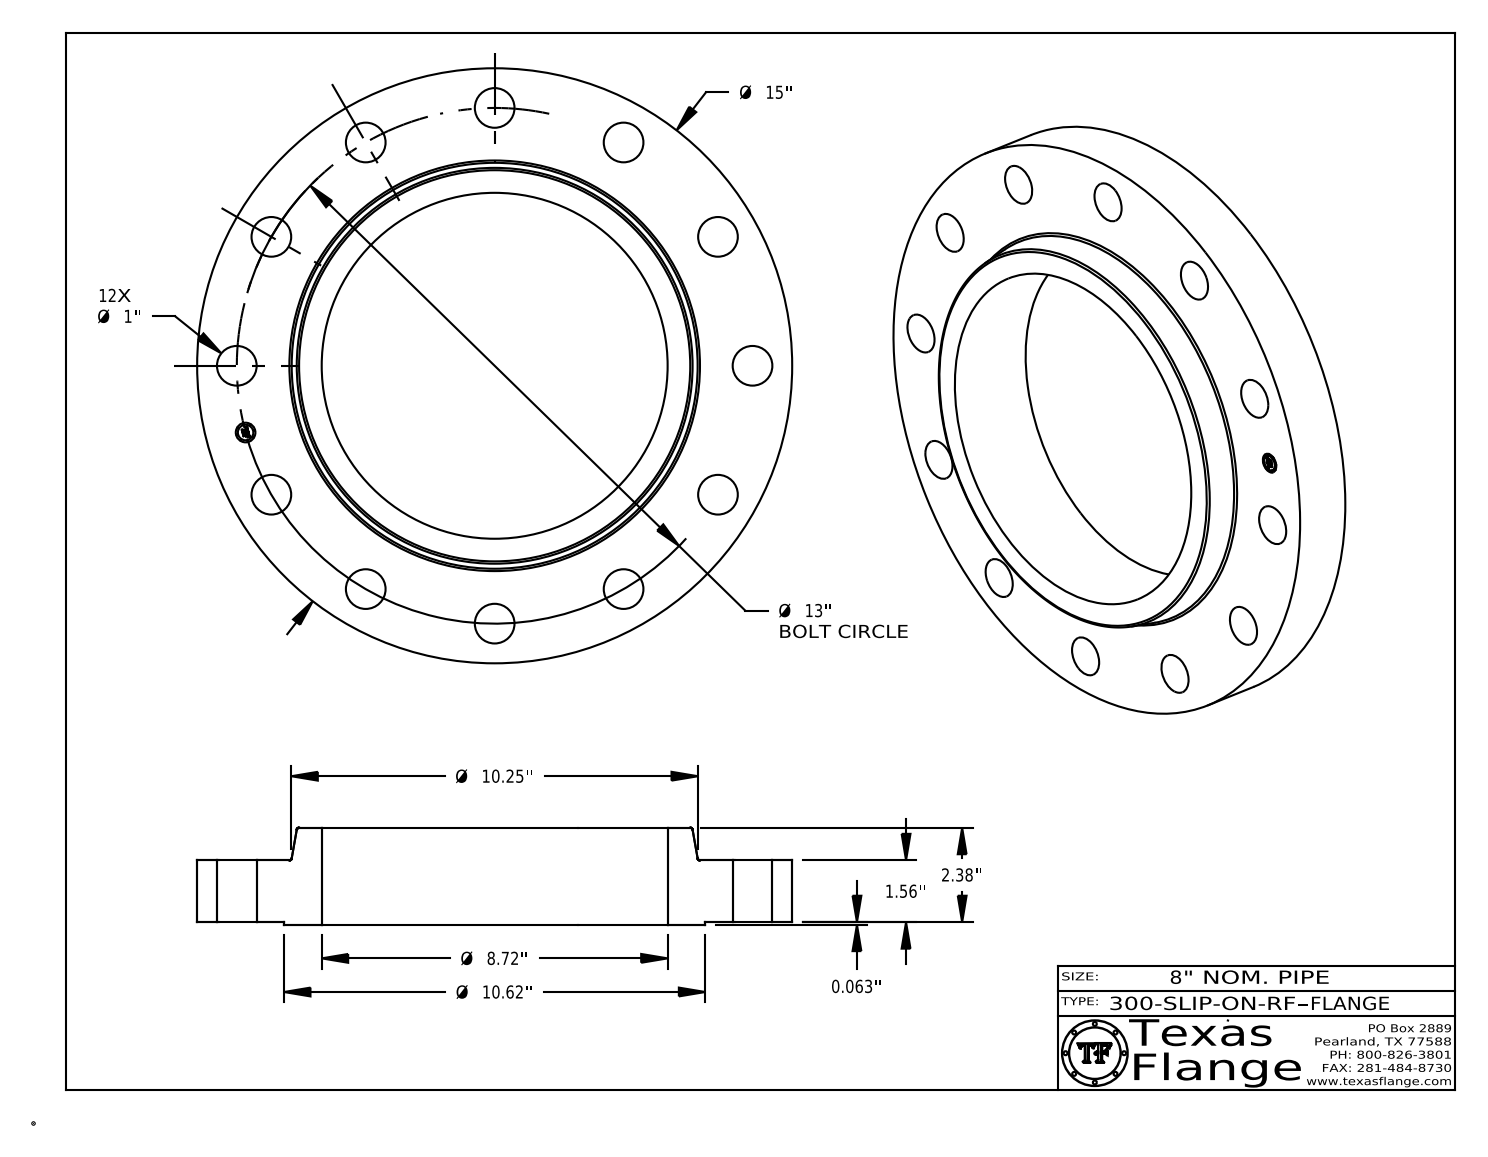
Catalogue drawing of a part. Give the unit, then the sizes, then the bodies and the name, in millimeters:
Units: millimetres
Overall size (bounding box): 381 × 381 × 62.1
Round holes (diameter × count): ⌀25.4 ×12, ⌀12.6 ×1, ⌀221.5 ×1
Round bosses / shafts (diameter × count): ⌀0.8 ×8, ⌀381 ×1, ⌀269.7 ×1, ⌀9.9 ×1
Main face-to-face distances: 39.6, 1.6, 41.2, 62.1, 60.5, 20.8, 40.8, 39.2, 0.4, 21.2
Hole centre spacings: 165.1, 85.5, 233.5, 286, 318.9, 330.2, 43.1, 126.4
Volume: 3 055 000 mm³ · Surface area: 282 100 mm²
Bodies: 1 solid, 425 faces (369 planar, 50 cylindrical, 6 other)
Part name (STEP PRODUCT): 300-SLIP-ON-RF
STEP written by: CATIA V5 STEP AP214 (AUTOMOTIVE_DESIGN)
